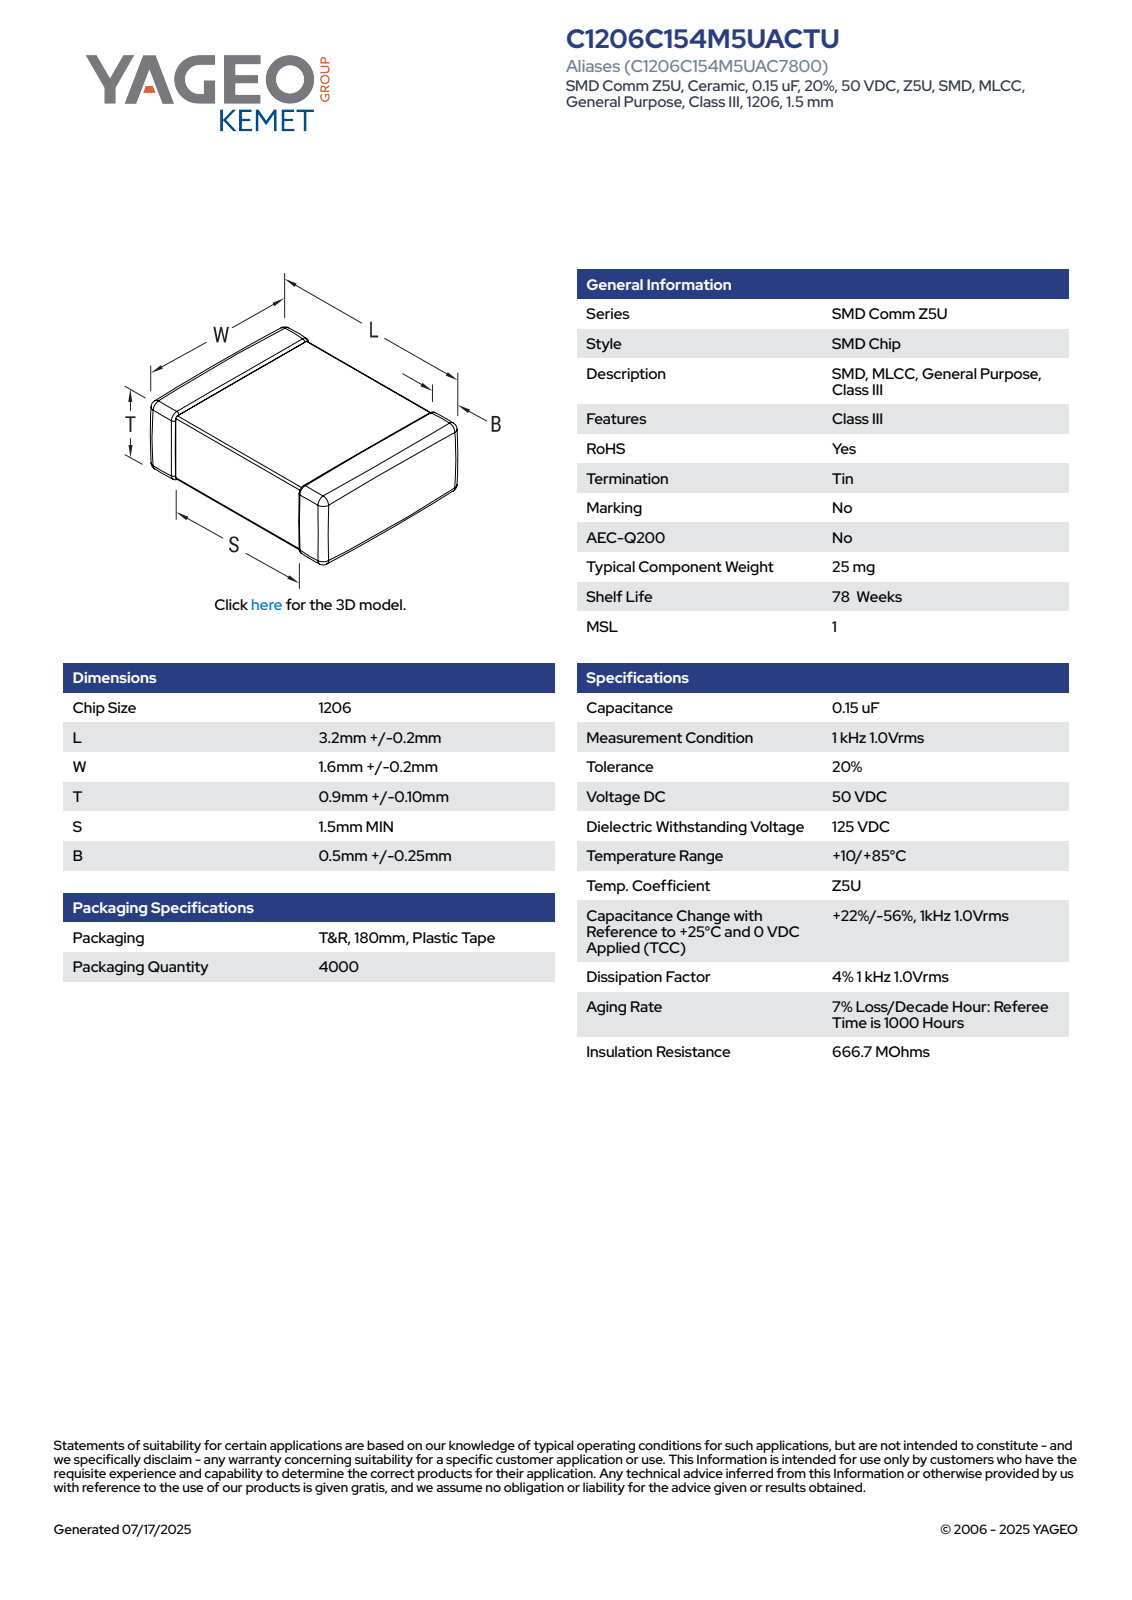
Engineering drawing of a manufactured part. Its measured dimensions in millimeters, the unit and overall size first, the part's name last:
Units: millimetres
Overall size (bounding box): 3.4 × 1.8 × 1
Main face-to-face distances: 0.96, 0.92, 1.76, 1, 1.72, 3.4, 1.8, 0.97, 0.93, 1.57
Volume: 6 mm³ · Surface area: 22 mm²
Bodies: 4 solids, 125 faces (71 planar, 38 cylindrical, 16 other)
Part name (STEP PRODUCT): CCS_CCSTD_1206_L3.4W1.8T1B0.5
STEP written by: SolidWorks 2021 (AUTOMOTIVE_DESIGN)
